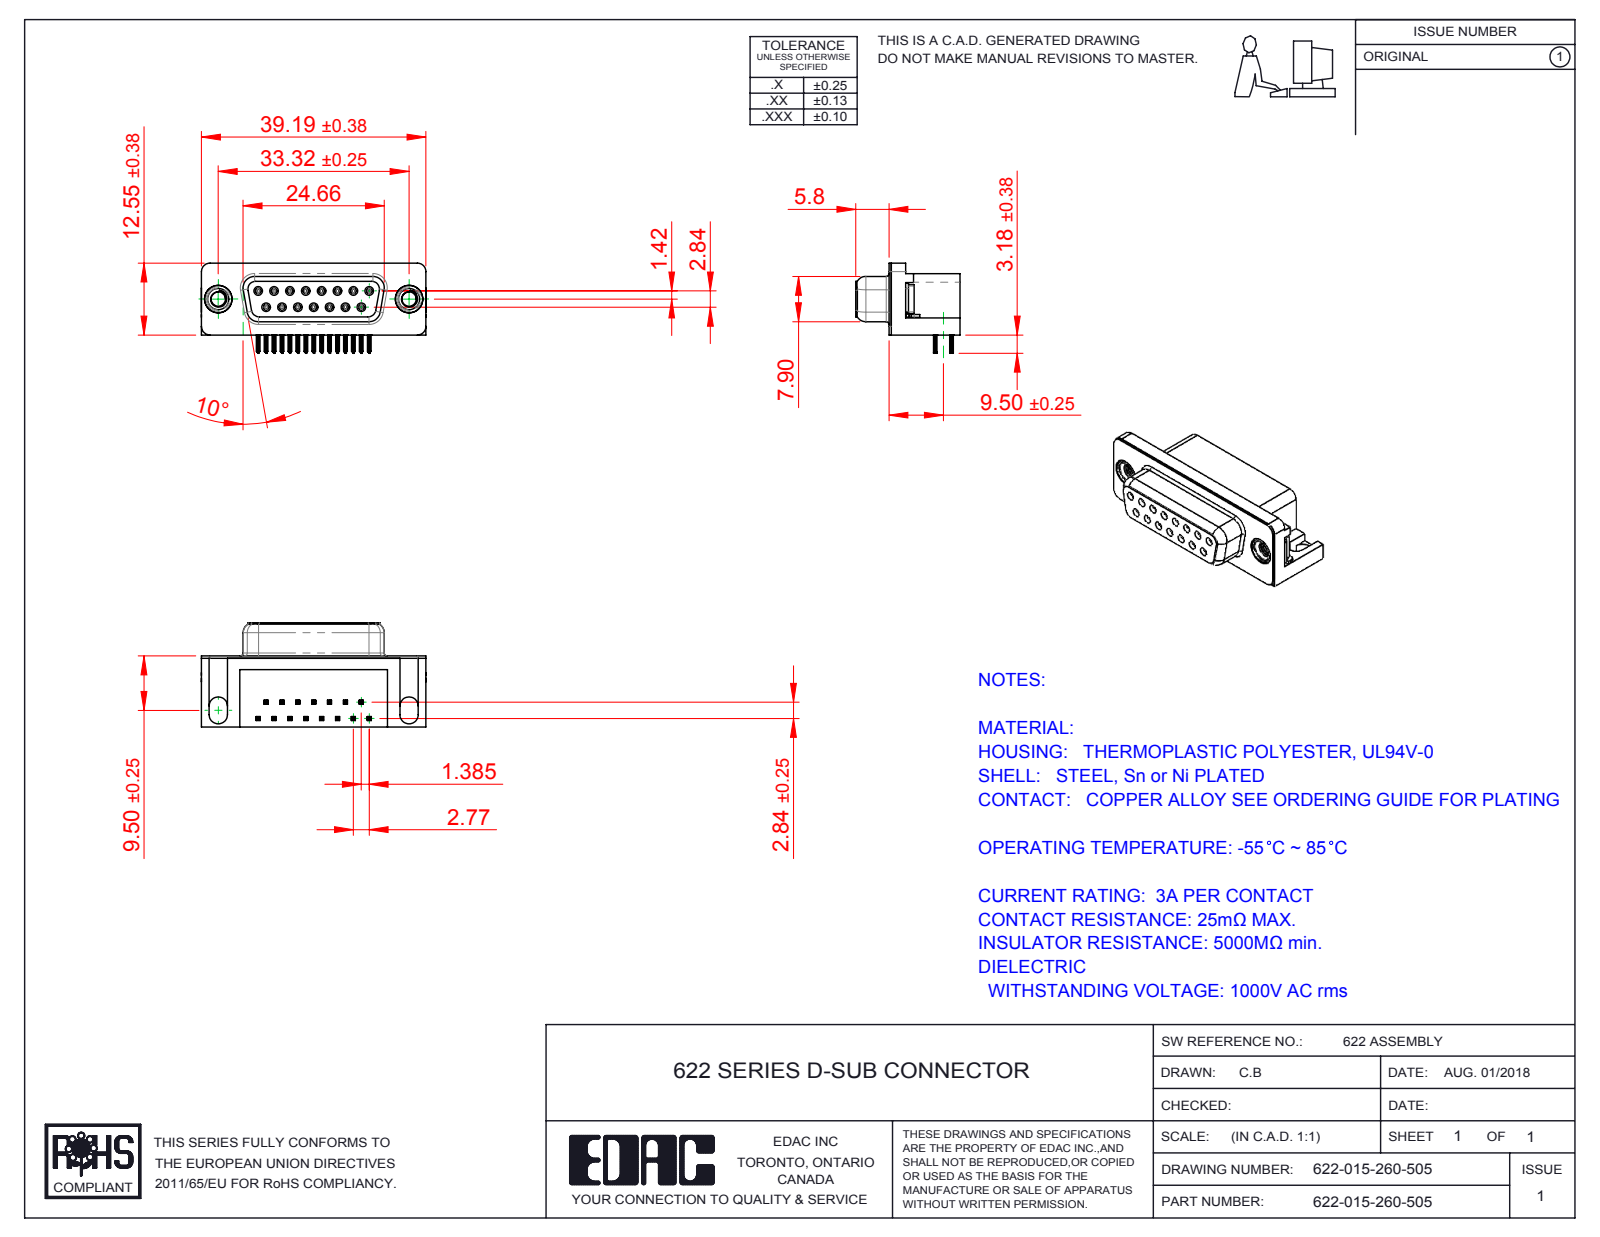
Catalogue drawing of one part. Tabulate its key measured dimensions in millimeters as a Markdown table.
| quantity | value |
| --- | --- |
| part name | 622-015-260-506; 622 Housing_15 Socket; 622 Non Board Mount; 622 M3 Threaded Rivet (+3 more) |
| STEP written by | SolidWorks 2016 (CONFIG_CONTROL_DESIGN) |
| units | millimeters |
| bodies | 21 solids, 2423 faces (1074 planar, 605 cylindrical, 744 other) |
| overall size | 39.22 × 18.2 × 15.73 |
| volume | 5 147 mm³ |
| surface area | 6 546 mm² |
| round holes (diameter × count) | 0.8 × 15, 0.9 × 15, 2.5 × 2, 4 × 2, 4.8 × 2, 5 × 2 |
| round bosses / shafts (diameter × count) | 1.2 × 15, 4.9 × 2, 4.75 × 2, 3.9 × 2 |
| partial cylindrical surfaces (radius × count) | 0.1 × 120, 0.15 × 60, 0.35 × 30, 1 × 18, 0.34 × 15, 0.25 × 8, 1.35 × 8, 1.5 × 8 |
| main face-to-face distances | 0.4, 12, 6.2, 12.4, 10.35, 2.9, 9.5, 2.5, 0.35, 0.45 |
| hole center spacings | 3.16, 2.77, 5.54, 8.31, 11.08, 5.03, 5.04, 7.48 |
